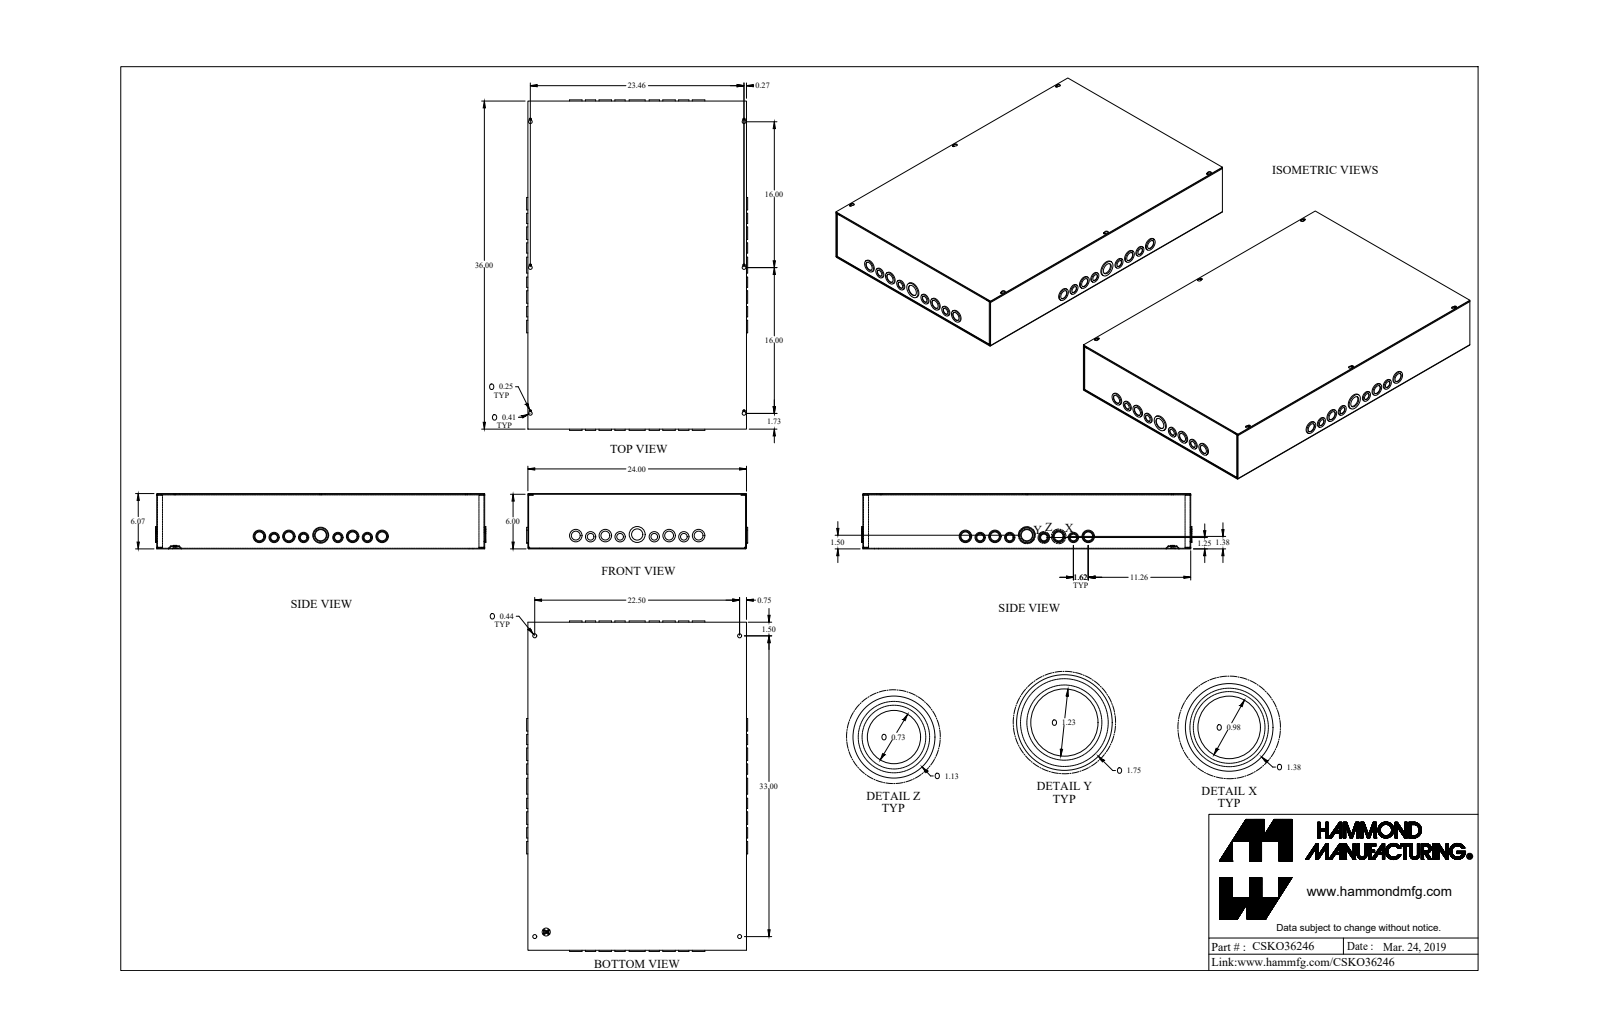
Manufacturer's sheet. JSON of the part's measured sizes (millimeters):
{"part_name": "CSKO36246_Default", "step_written_by": "SolidWorks 2019 (CONFIG_CONTROL_DESIGN)", "units": "millimeters", "bodies": {"solids": 4, "faces": 653, "planar": 273, "cylindrical": 372, "other": 8}, "overall_size": [921.1, 616.3, 154.2], "volume_mm3": 2999000, "surface_area_mm2": 3299000, "round_holes": [[24.9, 16], [31.3, 10], [18.6, 8], [4.3, 7], [11.1, 4], [40.8, 2], [12.7, 1]], "round_bosses_or_shafts": [[28.6, 14], [34.9, 9], [22.2, 8], [28.6, 4], [22.2, 4], [44.5, 2], [34.9, 1], [12.5, 1]], "partial_cylinders_radius": [[0.9, 12], [2.7, 12], [1.8, 8], [3.2, 6], [5.2, 6]], "face_to_face_distances": [1.8, 152.4, 150.6, 154.2, 607.8, 912.6, 609.6, 605.9, 914.4, 910.7], "hole_center_spacings": [41.3, 82.3, 219, 177.8, 260.1, 17.6, 48.2, 89]}
